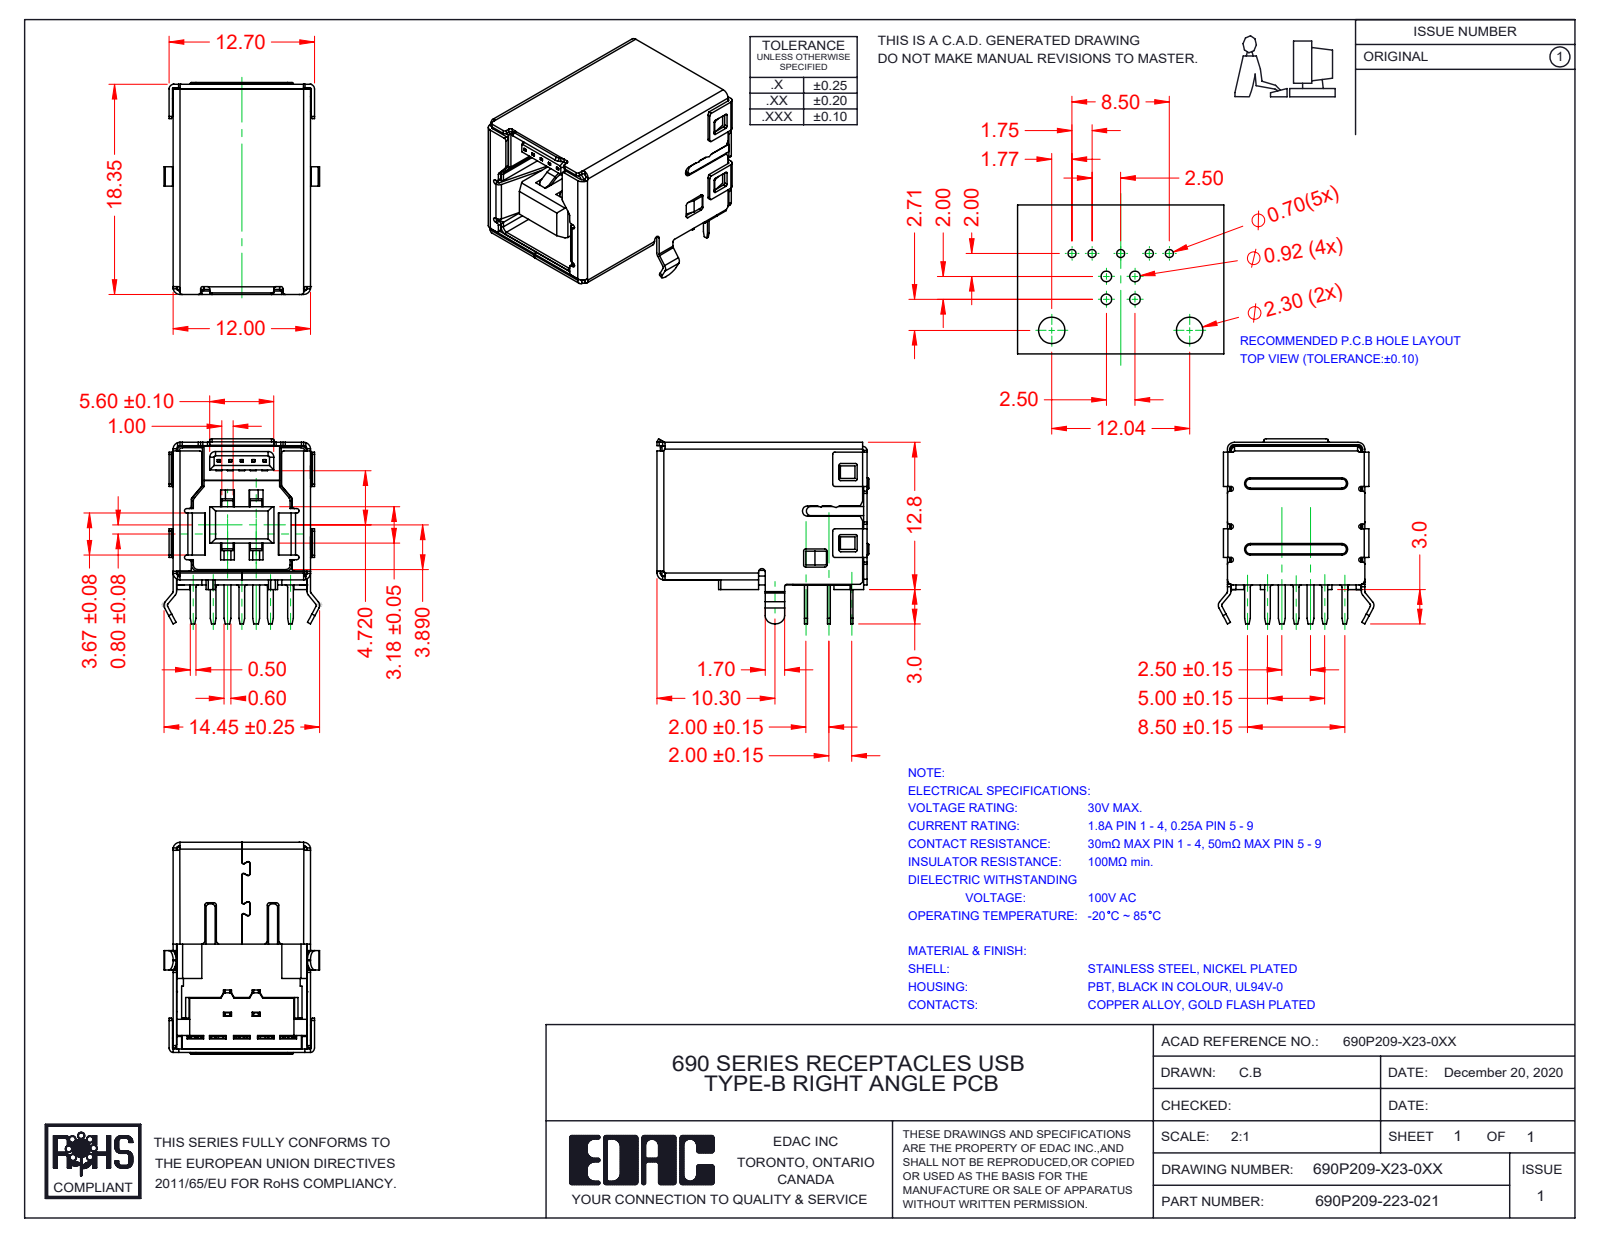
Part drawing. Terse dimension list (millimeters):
name: Contact9 690P209-X23-0XX; 690P209-123-011; Contact2 690P209-X23-0XX; Contact1 690P209-X23-0XX (+8 more)
written by: SolidWorks 2020 (AUTOMOTIVE_DESIGN)
unit: mm
bodies: 14 solids, 1459 faces (1032 planar, 353 cylindrical, 74 other)
size: 18.5 × 16.16 × 13.59
volume: 1 481 mm³; area: 5 358 mm²
rounds: 115× R0.2, 24× R0.5, 17× R0.1, 14× R0.15, 13× R0.3, 7× R0.4, 6× R0.6, 4× R0.38
face distances: 11.7, 11.38, 11.68, 0.32, 12, 11.4, 11.36, 3.03, 3.33, 3.2
